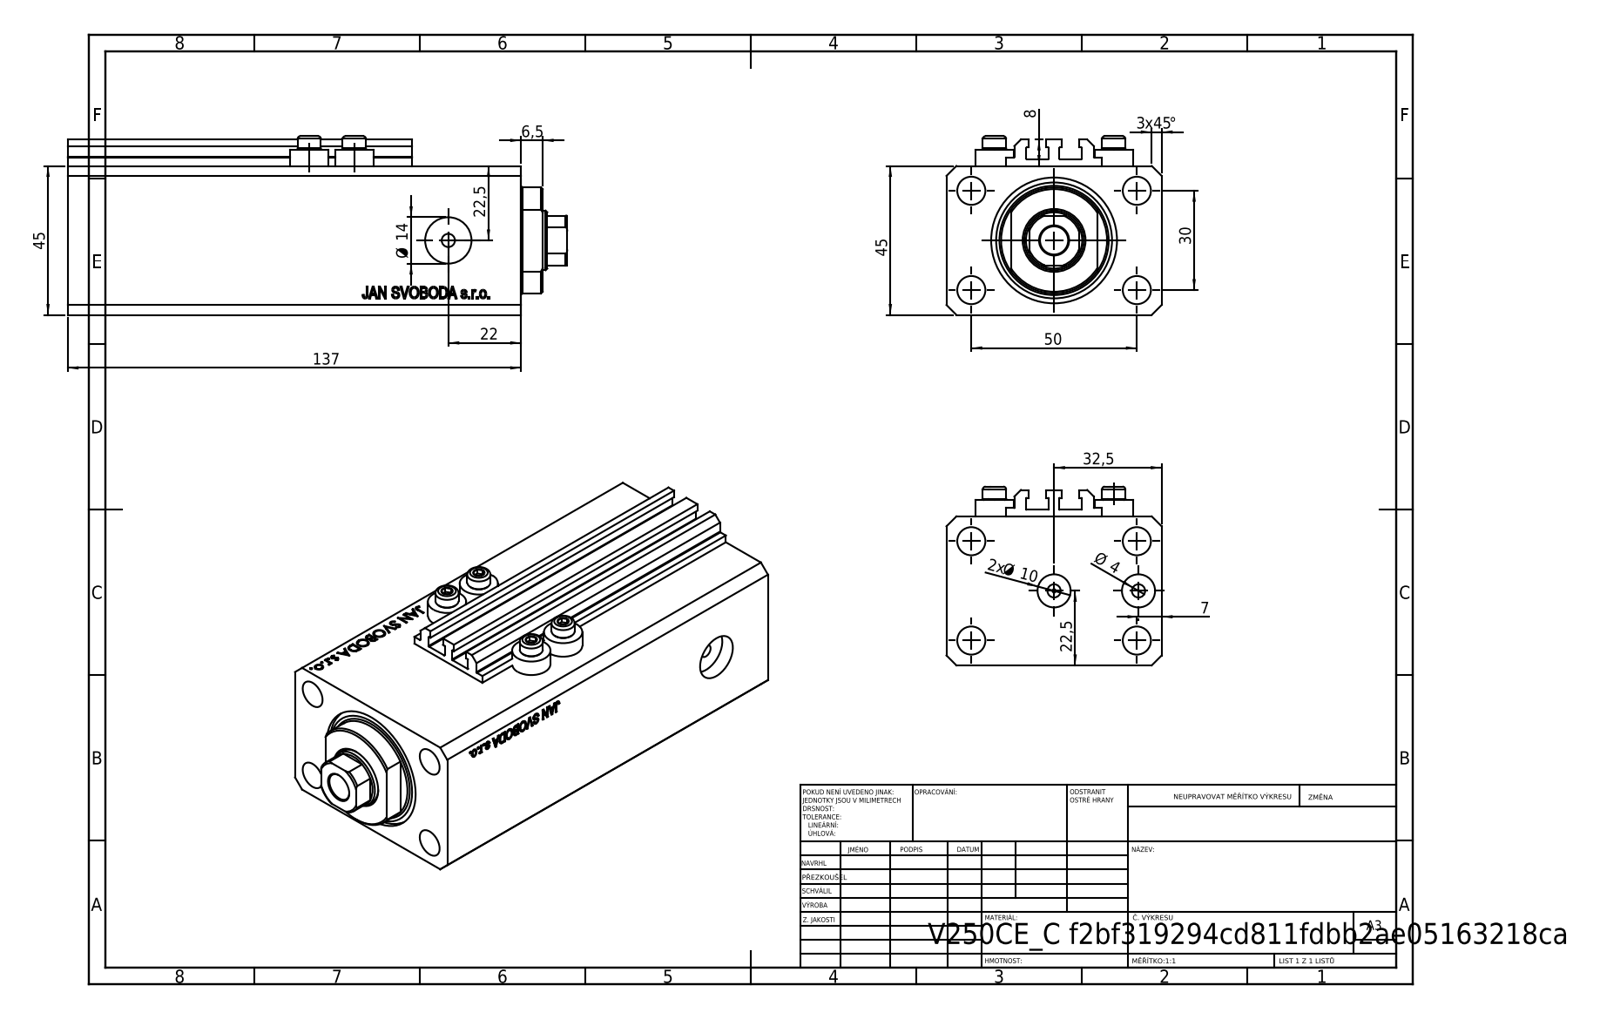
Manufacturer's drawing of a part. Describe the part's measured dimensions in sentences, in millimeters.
The part is named "V250CE_VC_C; V250CE_C_Body; V250CE_C_VCP; ALLEN BOLT V250CE". Its 3-D file was written by "SolidWorks 2019 (CONFIG_CONTROL_DESIGN)". It is 7 solids with 1036 faces: 502 planar, 88 cylindrical and 446 other. Overall it measures 150.9 by 65 by 54 millimeters. Its volume is 352 579 cubic millimeters and its surface area 92 244 square millimeters. Round holes: 8 of diameter 4, 5 of diameter 8.5, 2 of diameter 10, 2 of diameter 14, 1 of diameter 1.25, 1 of diameter 18, 1 of diameter 25, 1 of diameter 38. Round bosses or shafts: 4 of diameter 11.6, 4 of diameter 7. Partial cylindrical surfaces (rounded edges, fillets, slot ends): 10 of radius 0.2, 1 of radius 8.5, 1 of radius 16. The main face-to-face distances are 45, 65, 137, 111.9, 25.1, 2.5, 47, 73.52, 10, 53. The hole center spacings are 29.15, 13.6, 15.01, 30, 36, 38.48, 50, 52.68.
